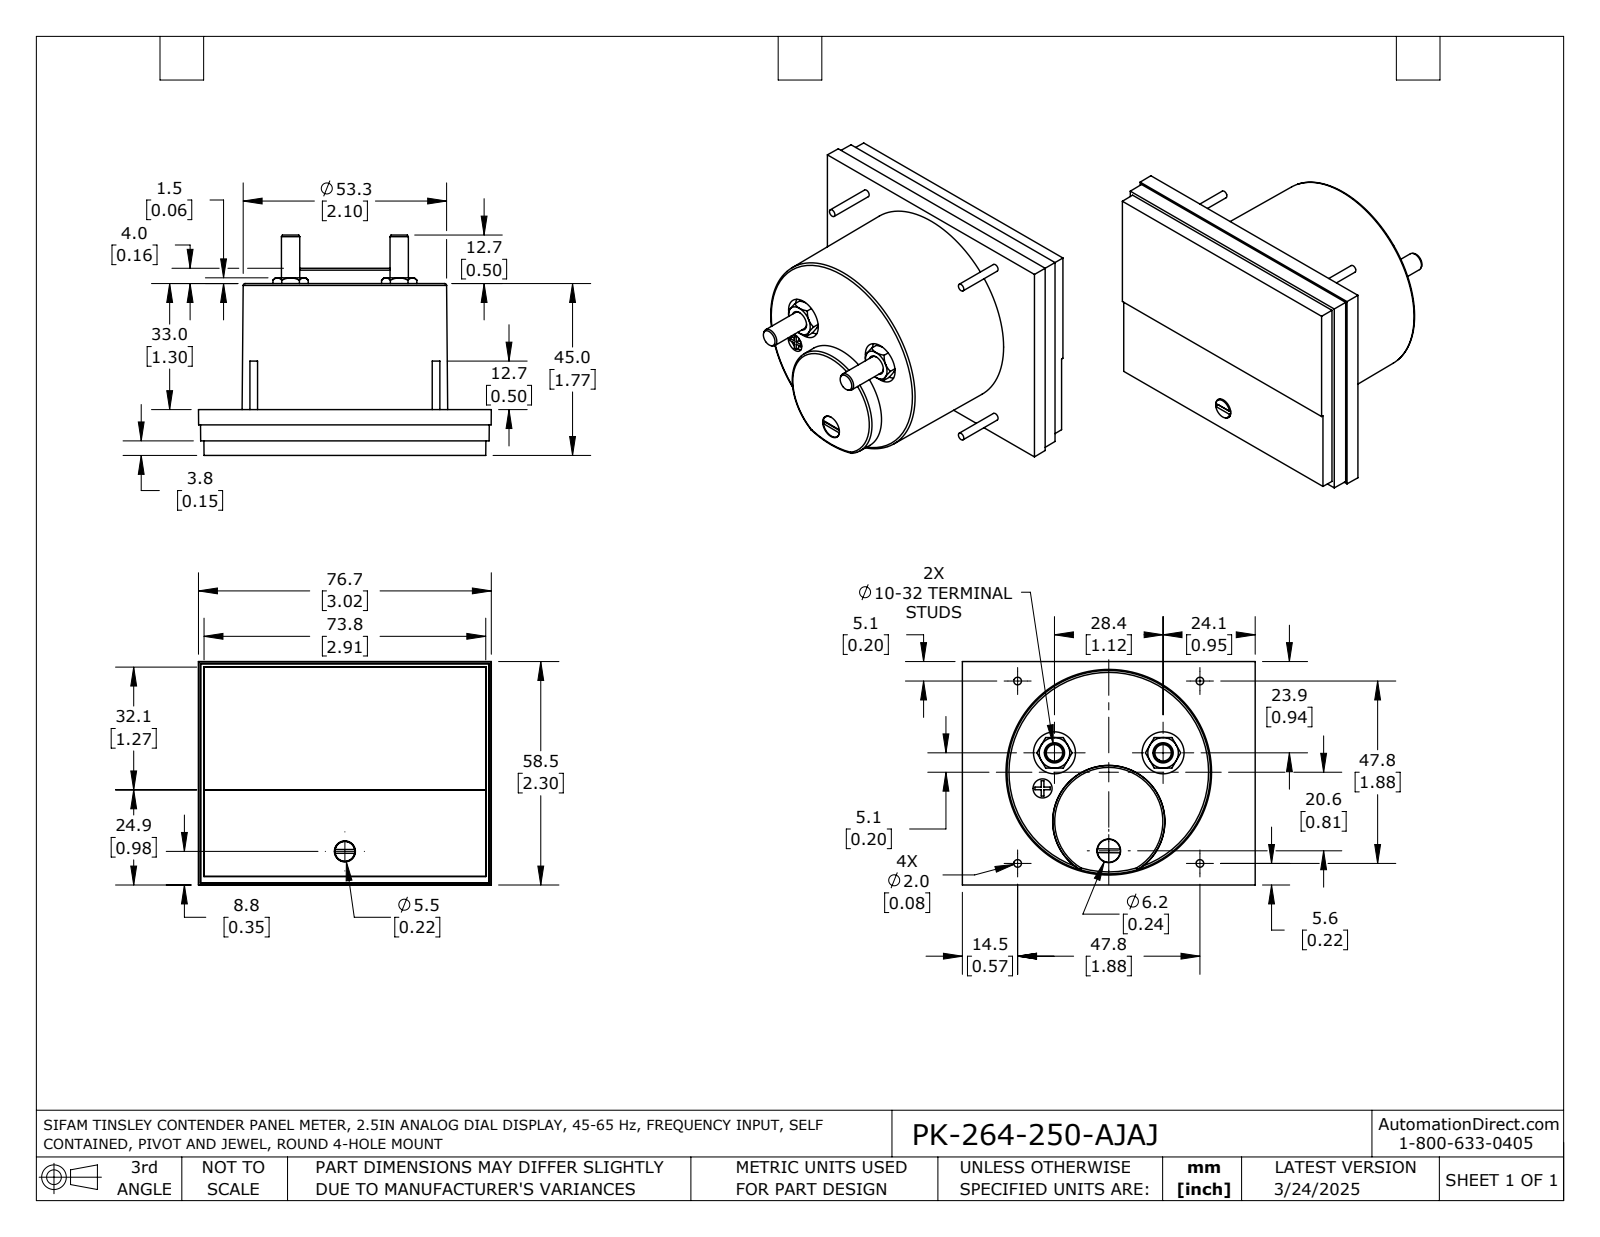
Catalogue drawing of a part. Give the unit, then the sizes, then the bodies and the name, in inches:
Units: inches
Overall size (bounding box): 3.02 × 2.303 × 2.272
Round holes (diameter × count): ⌀0.197 ×3, ⌀0.433 ×2, ⌀0.209 ×1, ⌀0.217 ×1, ⌀0.244 ×1
Round bosses / shafts (diameter × count): ⌀0.079 ×4, ⌀0.189 ×2, ⌀0.236 ×1, ⌀0.205 ×1
Partial cylindrical surfaces — rounded edges, fillets, slot ends (radius × count): R0.033 ×1
Main face-to-face distances: 0.02, 0.472, 0.13, 0.322, 0.15, 0.453, 0.057, 0.077, 0.396, 0.073
Hole centre spacings: 1.155, 1.16, 0.387, 0.938, 0.942, 1.12, 1.295
Volume: 7.657 in³ · Surface area: 36.55 in²
Bodies: 1 solid, 192 faces (95 planar, 37 cylindrical, 60 other)
Part name (STEP PRODUCT): PK-264-250-AJAJ
STEP written by: SolidWorks 2021 (AUTOMOTIVE_DESIGN)
